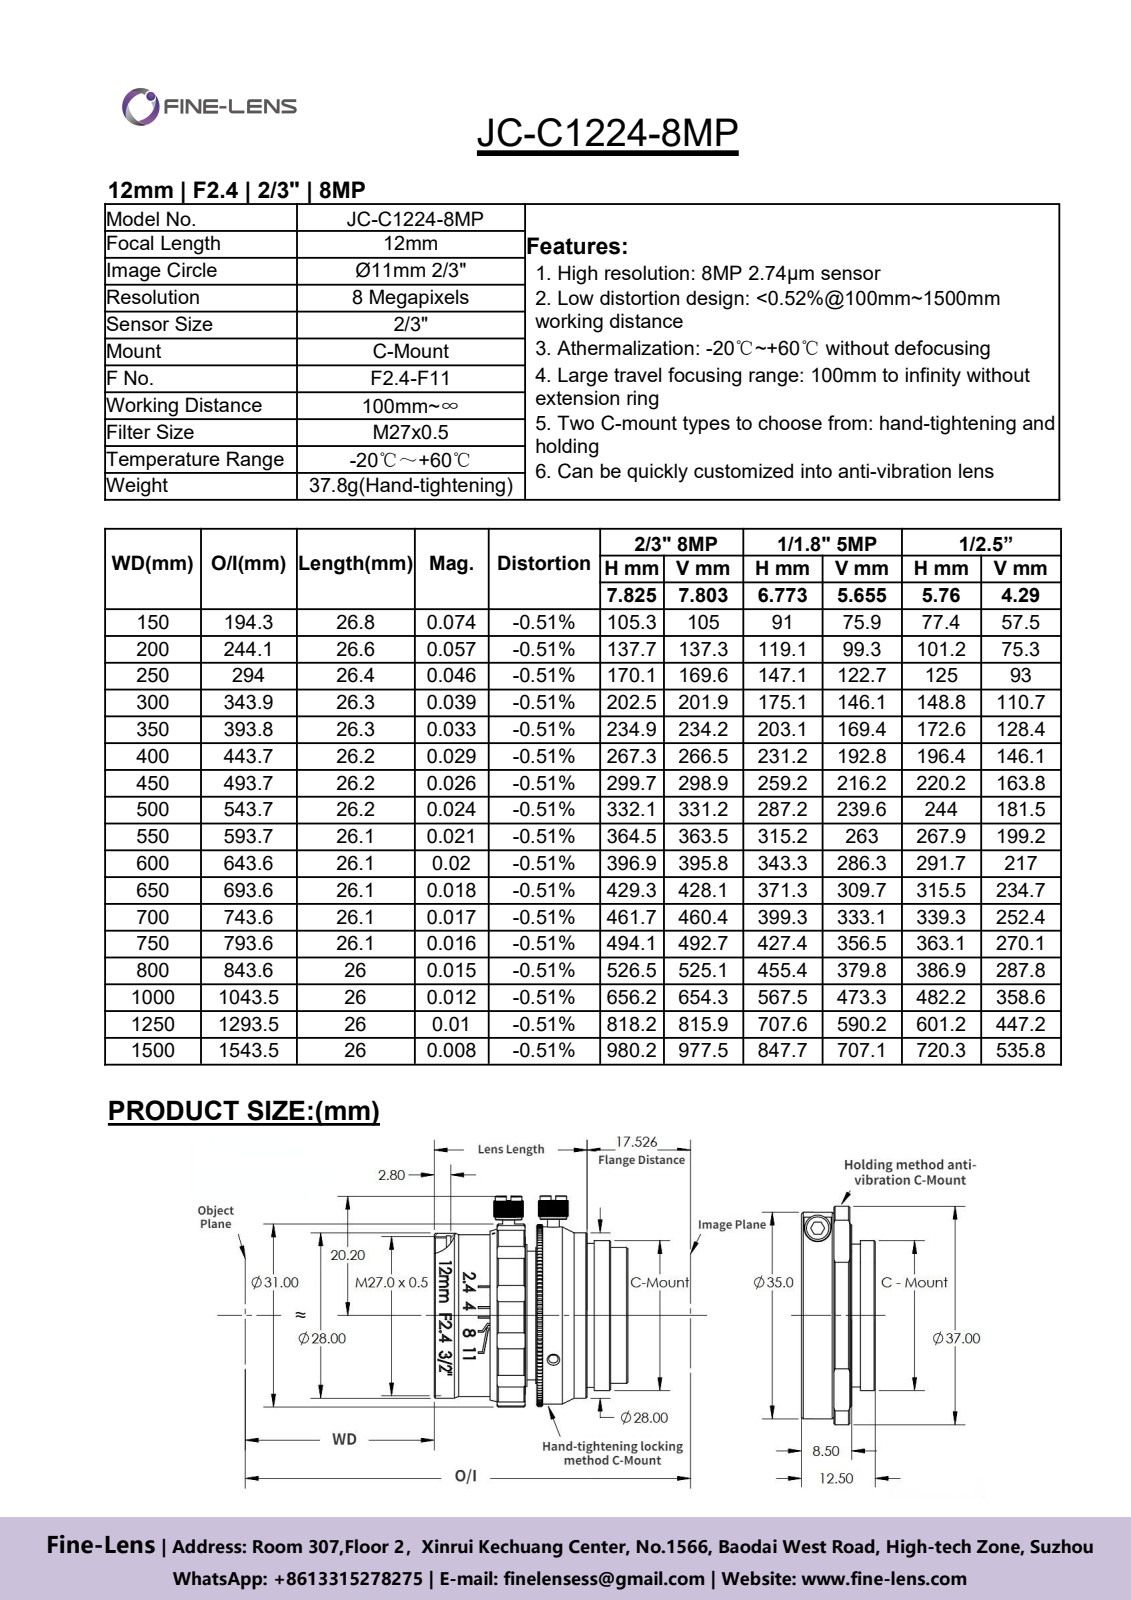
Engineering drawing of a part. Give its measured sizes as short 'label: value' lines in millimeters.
name: 1105
written by: SolidWorks 2018 (CONFIG_CONTROL_DESIGN)
unit: mm
bodies: 5 solids, 1933 faces (754 planar, 413 cylindrical, 766 other)
size: 35.7 × 32.8 × 31
volume: 18 052 mm³; area: 8 876 mm²
holes: 4× ⌀1.6, 1× ⌀0.5, 1× ⌀22.4, 1× ⌀24.2, 1× ⌀26.5, 1× ⌀27.2, 1× ⌀27.6, 1× ⌀29
bosses: 2× ⌀4.5, 2× ⌀2, 1× ⌀30, 1× ⌀28, 1× ⌀27.4, 1× ⌀25.4, 1× ⌀24.4, 1× ⌀24
rounds: 14× R2.5, 1× R1, 1× R13.65, 1× R13.95, 1× R15.4, 1× R15.5
face distances: 30, 15.71, 14.29, 7.35, 8.36, 22.65, 4.11, 11.6, 4.25, 18.4
hole spacings: 8.71
